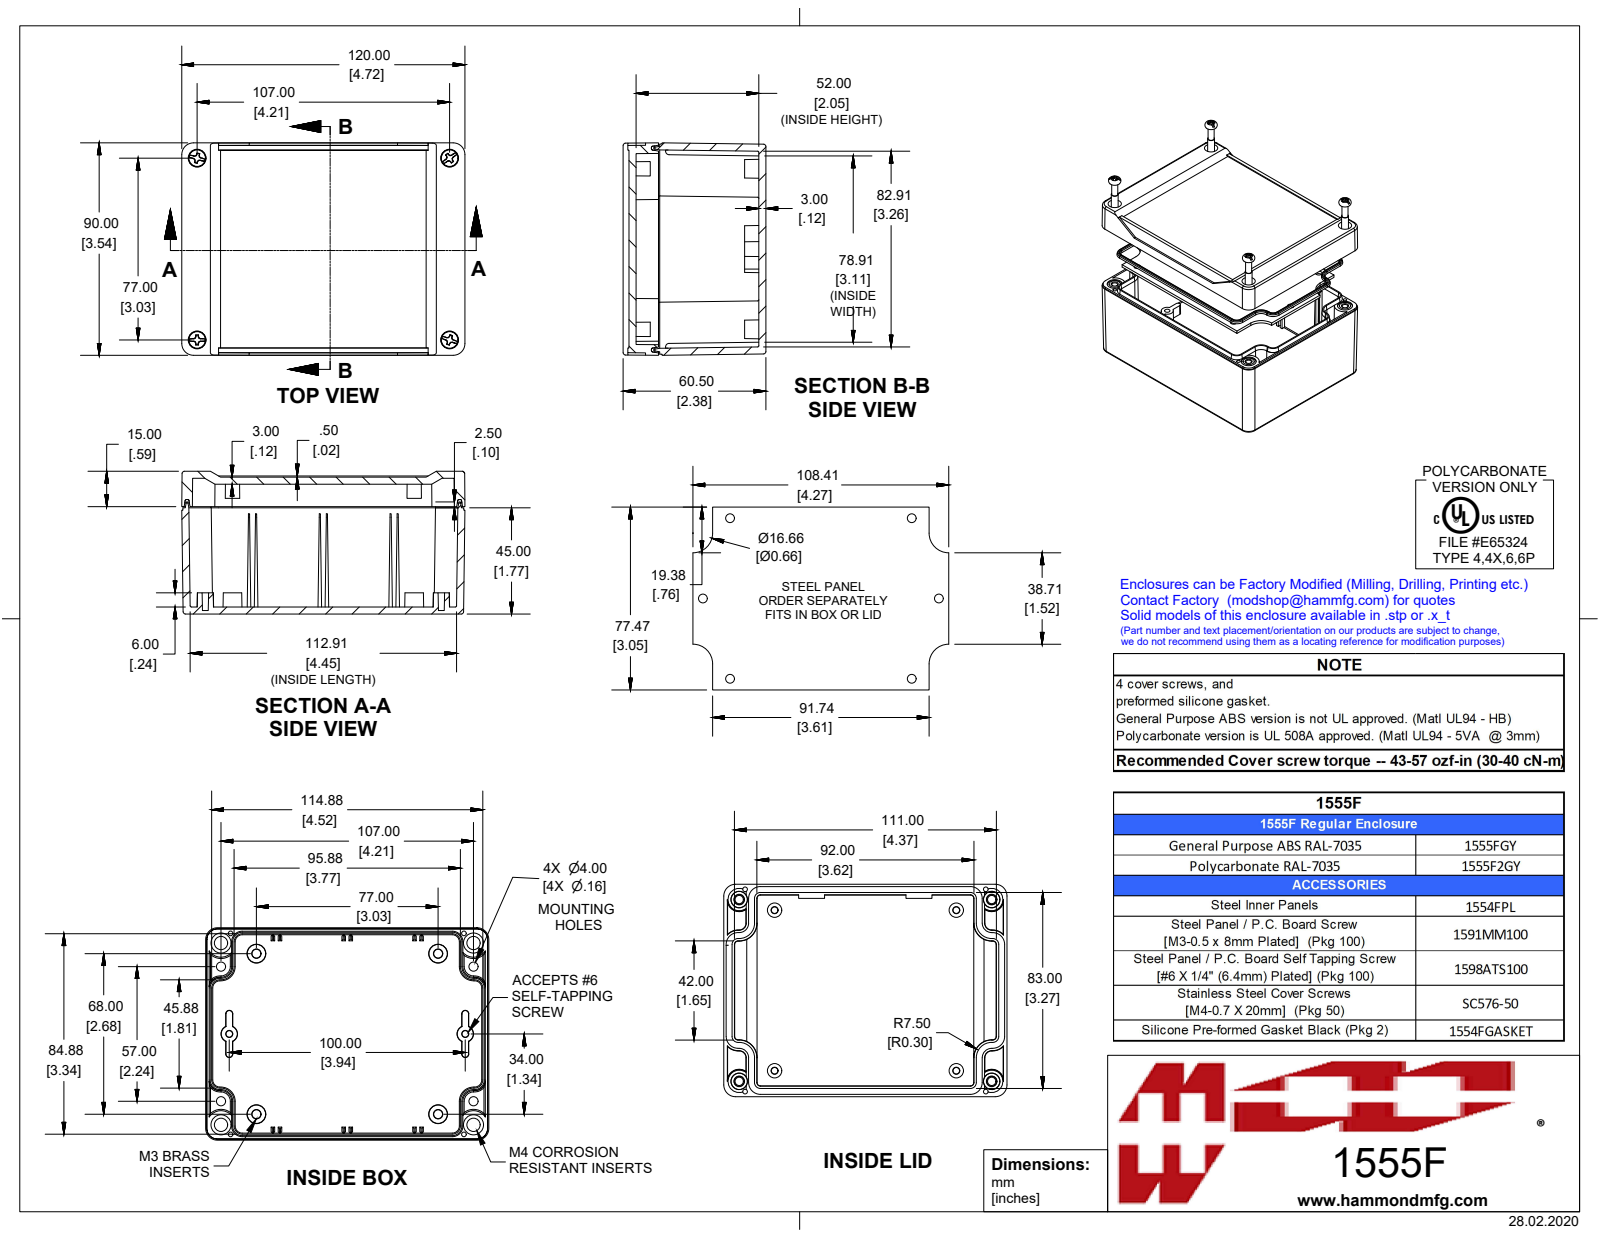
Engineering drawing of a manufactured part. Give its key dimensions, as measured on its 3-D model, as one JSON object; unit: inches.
{"part_name": "1555F2GY", "step_written_by": "SolidWorks 2019 (AUTOMOTIVE_DESIGN)", "units": "inches", "bodies": {"solids": 16, "faces": 1412, "planar": 440, "cylindrical": 346, "other": 626}, "overall_size": [4.724, 3.543, 2.382], "volume_in3": 9.968, "surface_area_in2": 200.6, "round_holes": [[0.079, 8], [0.097, 4], [0.128, 4], [0.138, 4], [0.147, 4], [0.276, 4], [0.335, 4], [0.11, 2]], "round_bosses_or_shafts": [[0.25, 4], [0.218, 4], [0.21, 4], [0.19, 4], [0.154, 4], [0.153, 4], [0.15, 4], [0.135, 4]], "partial_cylinders_radius": [[0.02, 24], [0.039, 8], [0.197, 8], [0.187, 4], [0.328, 4], [0.059, 3]], "face_to_face_distances": [0.118, 2.165, 0.354, 0.236, 0.419, 0.3, 0.064, 1.811, 1.929, 2.283], "hole_center_spacings": [0.197, 0.602, 0.617, 1.413, 1.522, 1.687, 2.915, 3.031]}
